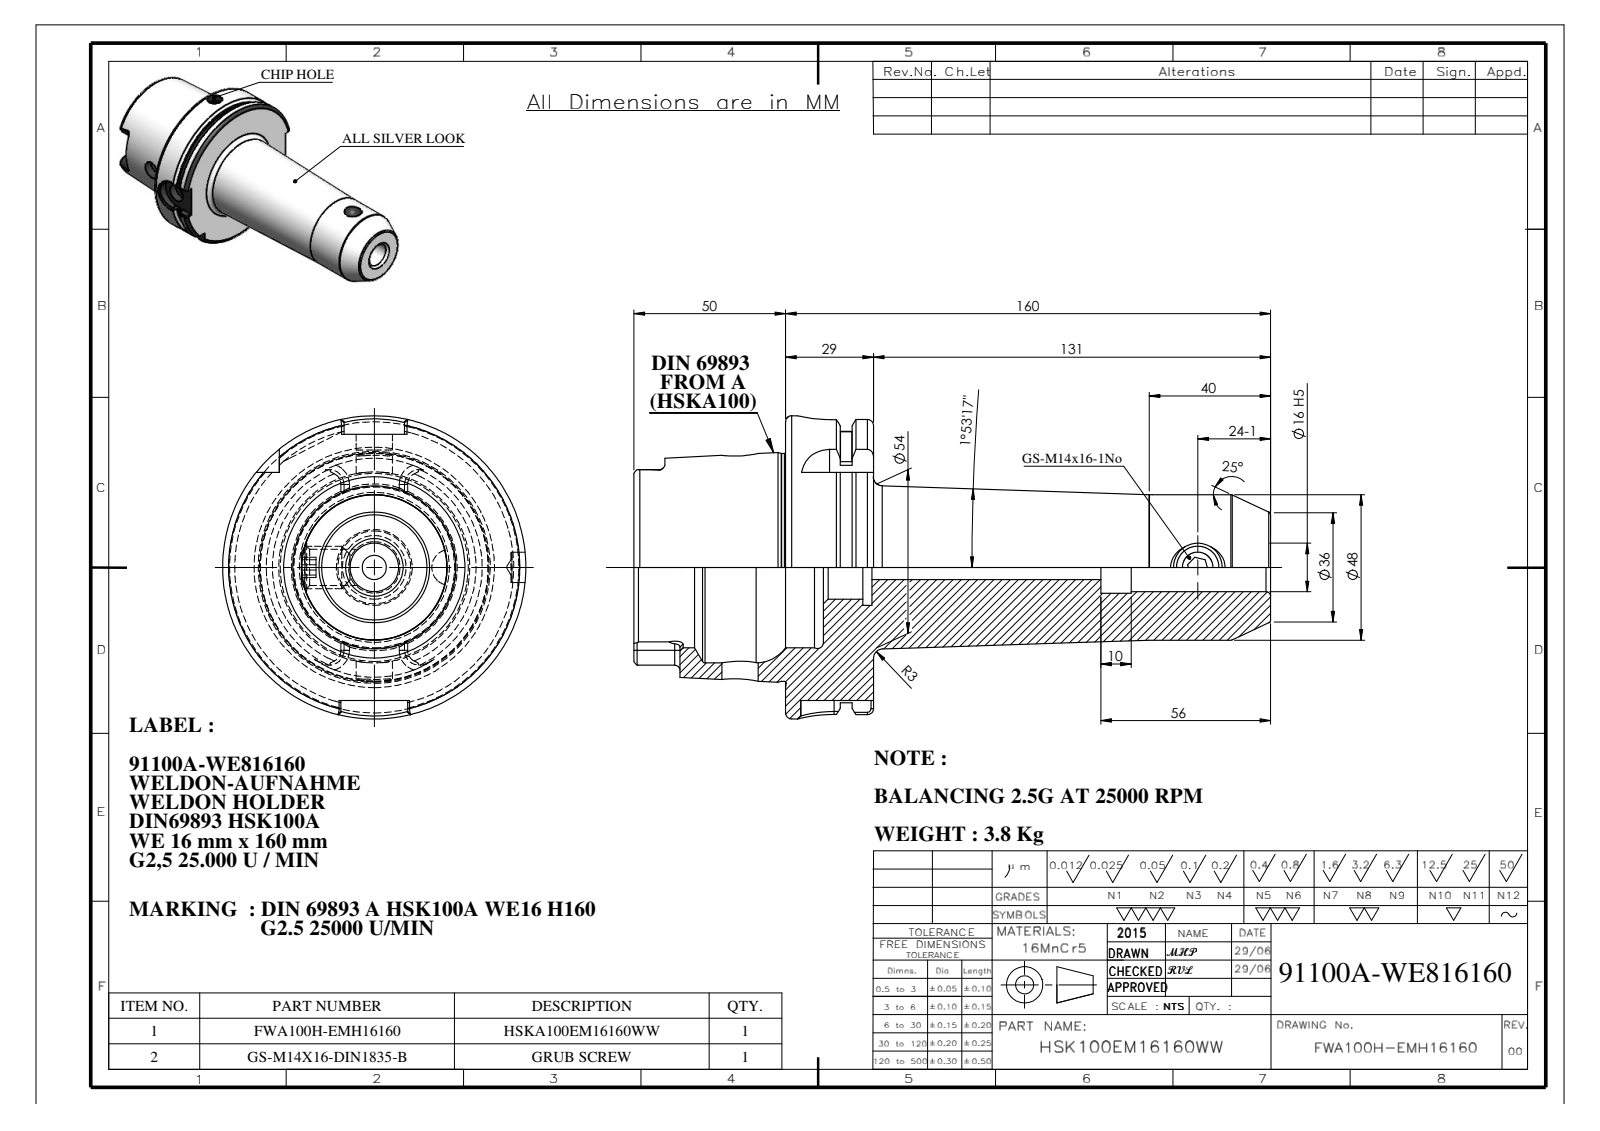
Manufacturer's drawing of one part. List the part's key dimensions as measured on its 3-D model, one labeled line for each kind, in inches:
Part name (STEP PRODUCT): HSKA100EM16160WW; GS-M14X16-DIN1835-B_ISO 4026 - M12 x 12-N; 91100A-WE816160
STEP written by: SolidWorks 2018 (CONFIG_CONTROL_DESIGN)
Units: inches
Bodies: 2 solids, 209 faces (64 planar, 58 cylindrical, 87 other)
Overall size (bounding box): 8.268 × 3.937 × 3.937
Volume: 30 in³ · Surface area: 116 in²
Round holes (diameter × count): ⌀0.472 ×3, ⌀0.63 ×2, ⌀0.315 ×1, ⌀0.394 ×1, ⌀0.669 ×1, ⌀0.827 ×1, ⌀0.984 ×1, ⌀2.087 ×1, ⌀2.48 ×1
Round bosses / shafts (diameter × count): ⌀3.937 ×1, ⌀3.622 ×1, ⌀2.959 ×1, ⌀1.89 ×1, ⌀0.551 ×1
Partial cylindrical surfaces — rounded edges, fillets, slot ends (radius × count): R0.071 ×6, R0.192 ×4, R0.394 ×2, R0.433 ×1
Main face-to-face distances: 1.142, 0.492, 0.65, 1.969, 2.461, 3.11, 8.268, 6.299, 5.807, 5.157
Hole centre spacings: 1.181, 5.079
